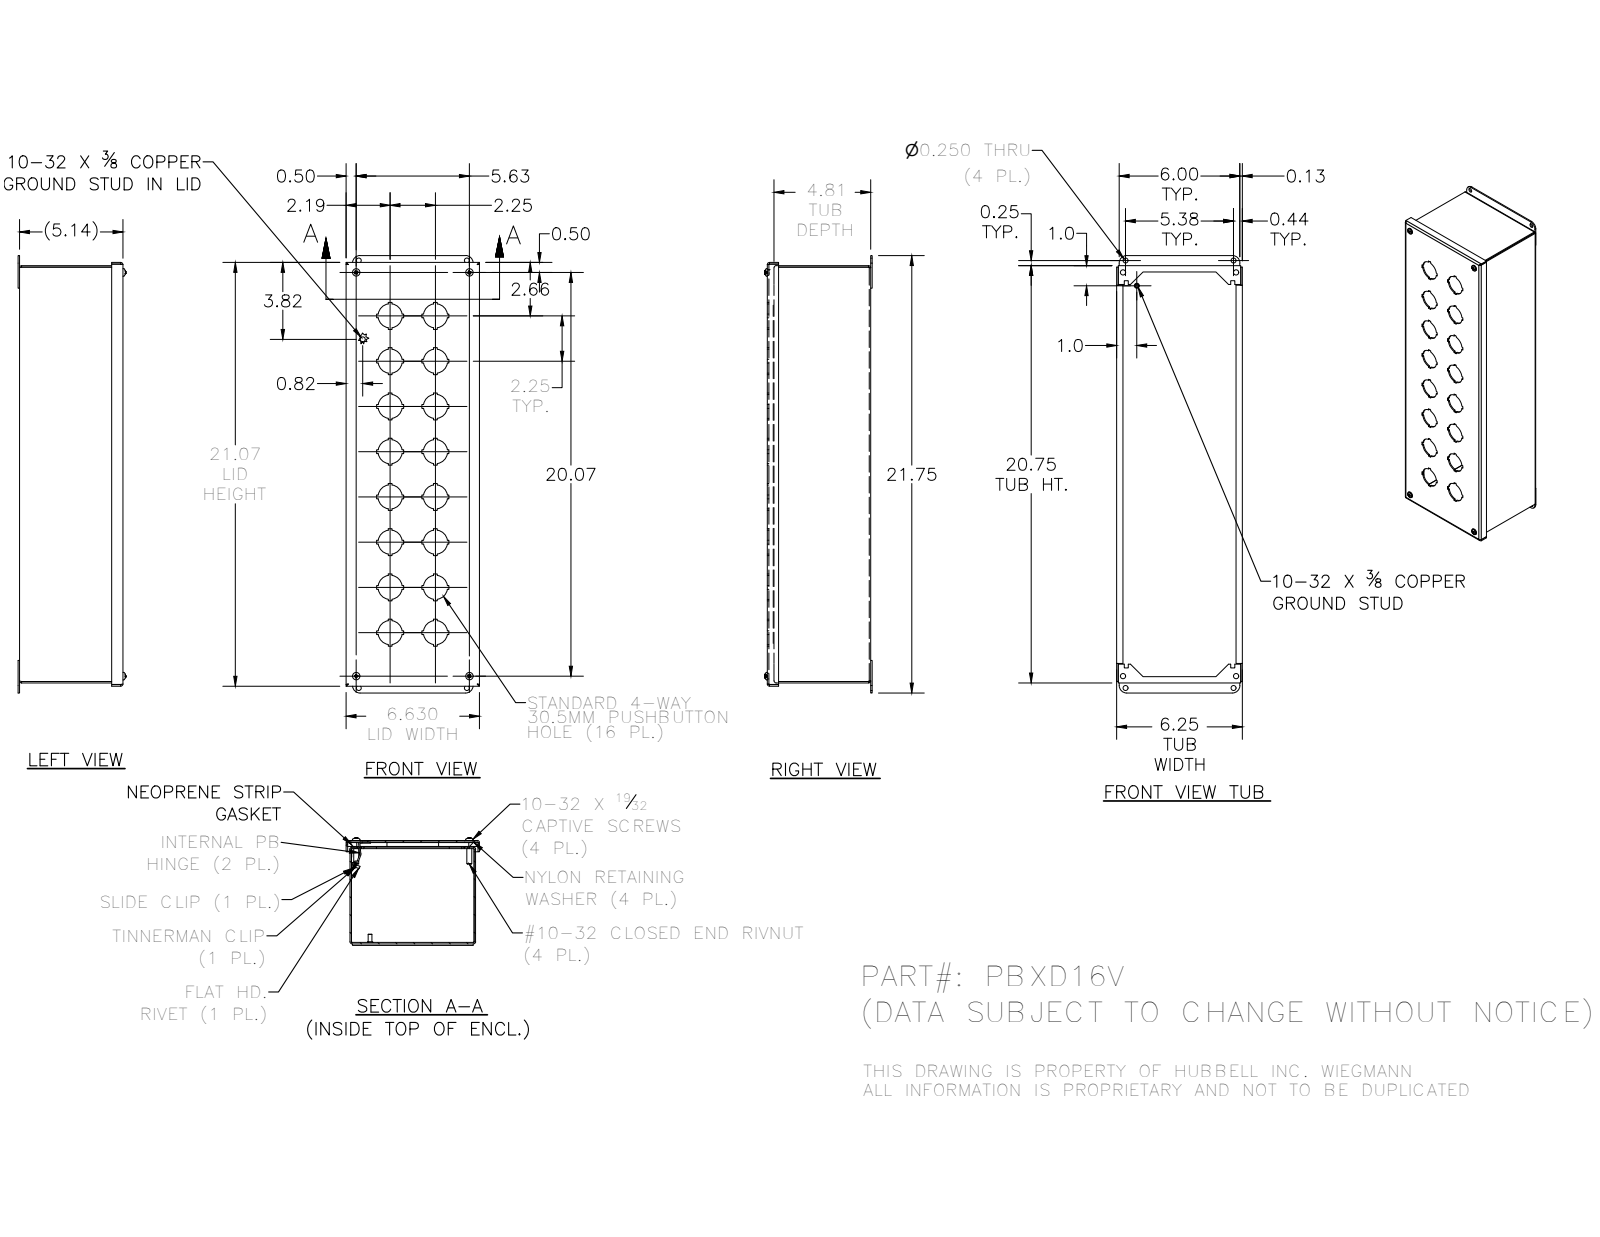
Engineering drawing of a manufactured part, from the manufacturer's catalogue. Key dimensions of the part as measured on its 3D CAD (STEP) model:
Part name (STEP PRODUCT): PBXD16VLID; 372163; 39077; PBXD16VBKP (+8 more)
STEP written by: Autodesk Inventor 2016 (AUTOMOTIVE_DESIGN)
Units: millimetres
Bodies: 31 solids, 897 faces (587 planar, 196 cylindrical, 114 other)
Overall size (bounding box): 552.45 × 168.4 × 135.79
Volume: 770 286 mm³ · Surface area: 795 552 mm²
Round holes (diameter × count): ⌀30.48 ×16, ⌀3.96 ×4, ⌀4.98 ×4, ⌀6.35 ×4, ⌀6.53 ×4, ⌀7.06 ×4, ⌀7.14 ×4, ⌀7.95 ×4, ⌀3.56 ×2
Round bosses / shafts (diameter × count): ⌀4.83 ×6, ⌀11.51 ×4, ⌀10.31 ×4, ⌀9.47 ×4, ⌀6.3 ×4, ⌀6.35 ×3, ⌀3.17 ×1
Partial cylindrical surfaces — rounded edges, fillets, slot ends (radius × count): R0.79 ×12, R2.67 ×12, R4.78 ×6, R2.27 ×4, R2.29 ×4, R9.53 ×4, R0.8 ×3, R1.59 ×3
Main face-to-face distances: 1.88, 128.73, 156.87, 130.61, 126.85, 158.75, 154.99, 525.17, 0.81, 4.78
Hole centre spacings: 57.15, 80.82, 114.3, 127.79, 171.45, 180.72, 228.6, 235.64
